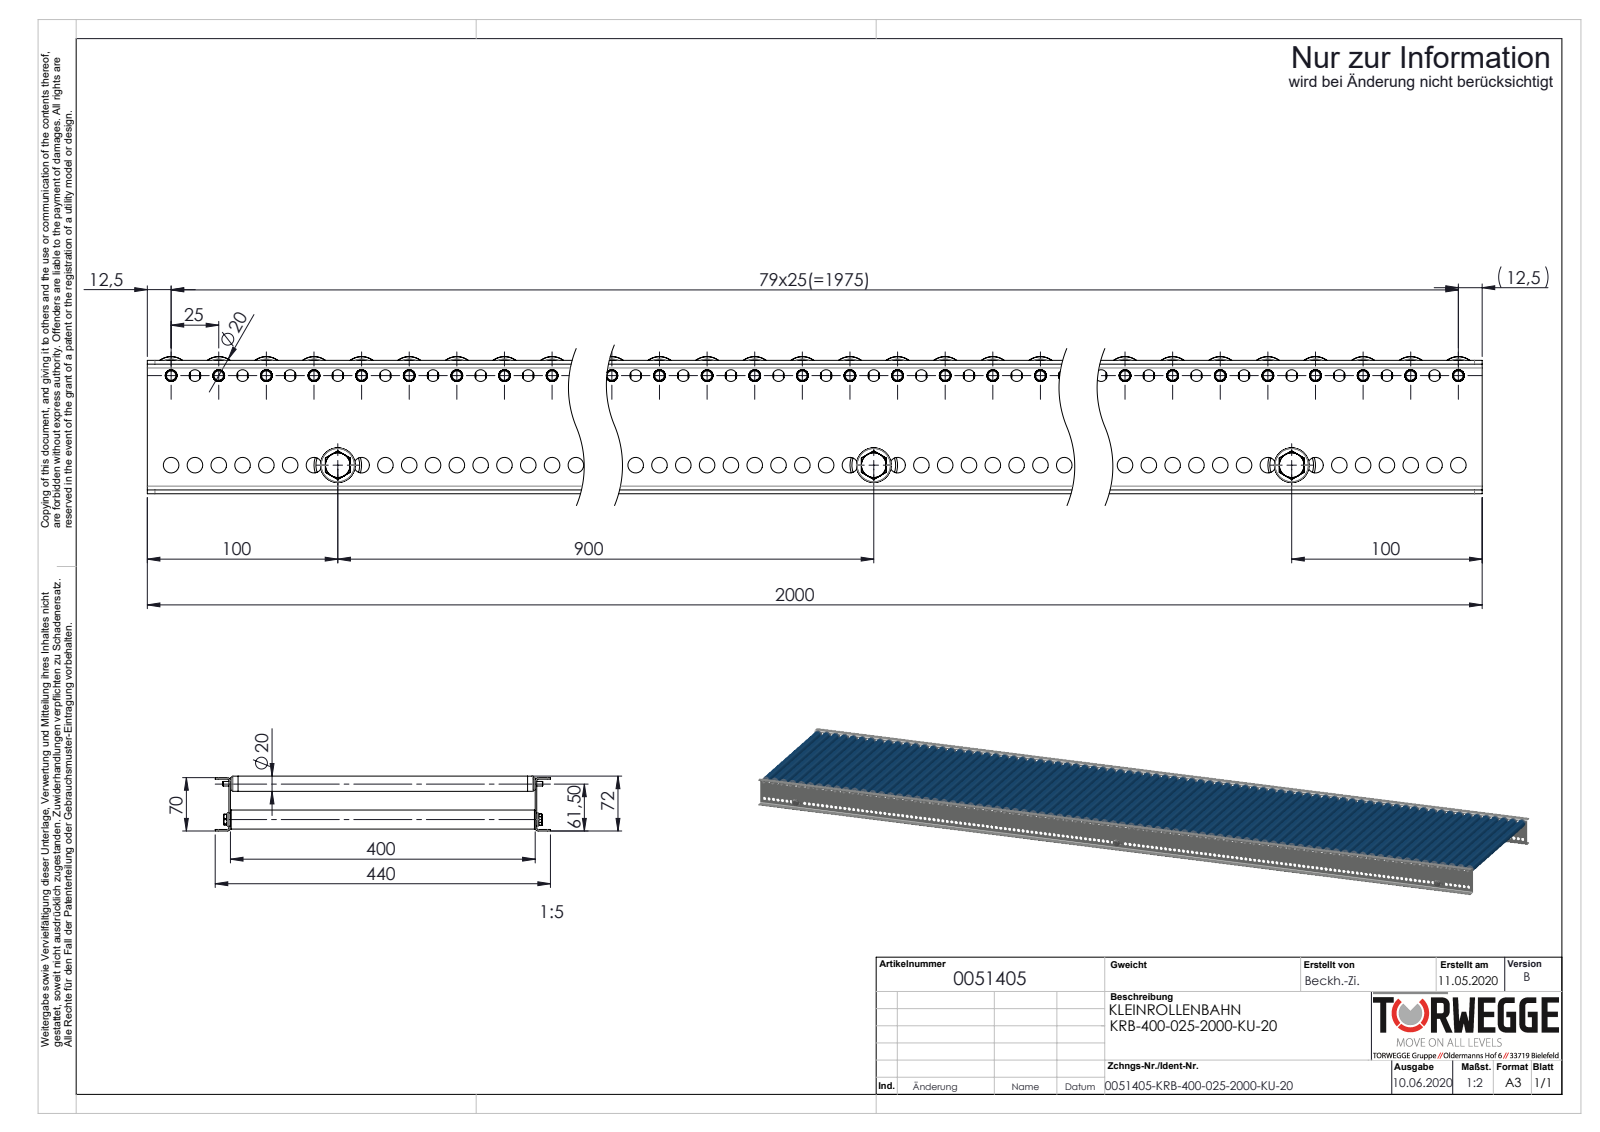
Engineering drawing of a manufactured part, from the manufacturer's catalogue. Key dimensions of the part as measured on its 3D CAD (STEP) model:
Part name (STEP PRODUCT): 0017012_Tragrollenrohr-Ø20x1,5KU_KFG_L380; 0051405; KUT50-20x1,5-KU-A6_FA-EL=KFG_L=400; 0039777_Achse-Ø06-FA-KFG_L=420 fr D20 (+4 more)
STEP written by: SolidWorks 2020 (AUTOMOTIVE_DESIGN)
Units: millimetres
Bodies: 497 solids, 21168 faces (7030 planar, 7890 cylindrical, 6248 other)
Overall size (bounding box): 2000 × 440 × 71
Volume: 5 535 000 mm³ · Surface area: 5 806 000 mm²
Round holes (diameter × count): ⌀6.2 ×159, ⌀8.2 ×159, ⌀6.1 ×80, ⌀12.4 ×80, ⌀13.2 ×80, ⌀14.6 ×80, ⌀16.2 ×80, ⌀17 ×80, ⌀17.2 ×80, ⌀6.8 ×3
Round bosses / shafts (diameter × count): ⌀20 ×80, ⌀19.9 ×80, ⌀17.1 ×80, ⌀16.8 ×80, ⌀16.5 ×80, ⌀11.4 ×80, ⌀11.1 ×80, ⌀10.2 ×80
Partial cylindrical surfaces — rounded edges, fillets, slot ends (radius × count): R4.05 ×80, R4 ×8, R2 ×4
Main face-to-face distances: 2, 402, 68, 400, 404, 70, 66, 392, 10, 12
Hole centre spacings: 12.5, 25, 37.5, 50, 62.5, 75, 87.5, 100
